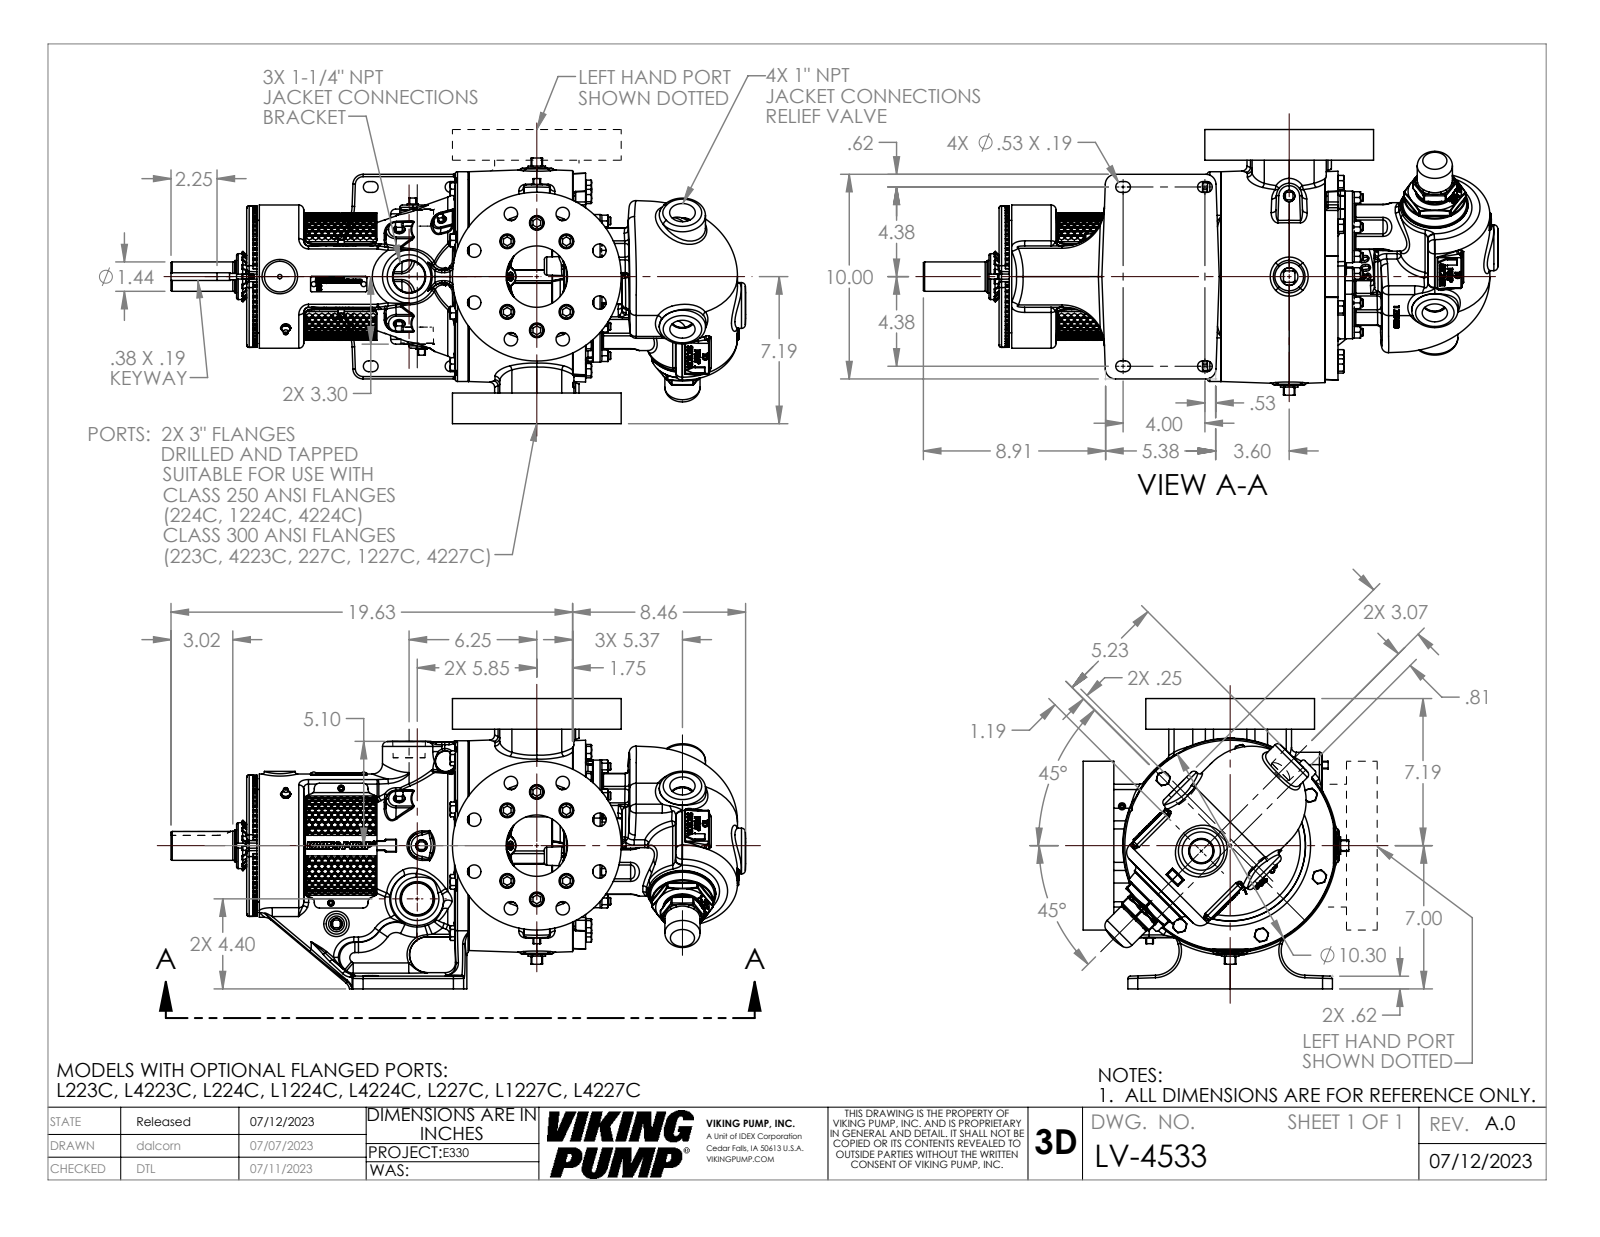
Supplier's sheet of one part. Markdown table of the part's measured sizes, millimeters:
| quantity | value |
| --- | --- |
| part name | LV-4533 |
| STEP written by | SolidWorks 2024 (AUTOMOTIVE_DESIGN) |
| units | millimeters |
| bodies | 1 solid, 5652 faces (1848 planar, 1019 cylindrical, 2785 other) |
| overall size | 712.7 × 360.4 × 331.5 |
| volume | 20 710 000 mm³ |
| surface area | 1 111 000 mm² |
| round holes (diameter × count) | 16.7 × 16, 11.9 × 12, 18.3 × 12, 27.8 × 8, 5.1 × 6, 6.4 × 6, 4 × 3, 6.8 × 2, 8 × 2, 76.2 × 2, 11.5 × 1, 40.1 × 1 |
| round bosses / shafts (diameter × count) | 11.1 × 15, 16.8 × 12, 15.9 × 9, 9.4 × 8, 15.9 × 6, 88.9 × 3, 7.9 × 3, 209.6 × 2 |
| partial cylindrical surfaces (radius × count) | 1.6 × 109, 3 × 82, 1.8 × 74, 0.8 × 34, 12.7 × 34, 6.1 × 16, 25.4 × 16, 4.8 × 14 |
| main face-to-face distances | 38.1, 360.3, 322.2, 57.2, 350.3, 89.8, 260.5, 69.9, 12.7, 54.4 |
| hole center spacings | 84.2, 119, 76.2, 64.4, 34.9, 34.2, 42.6, 55.4 |
